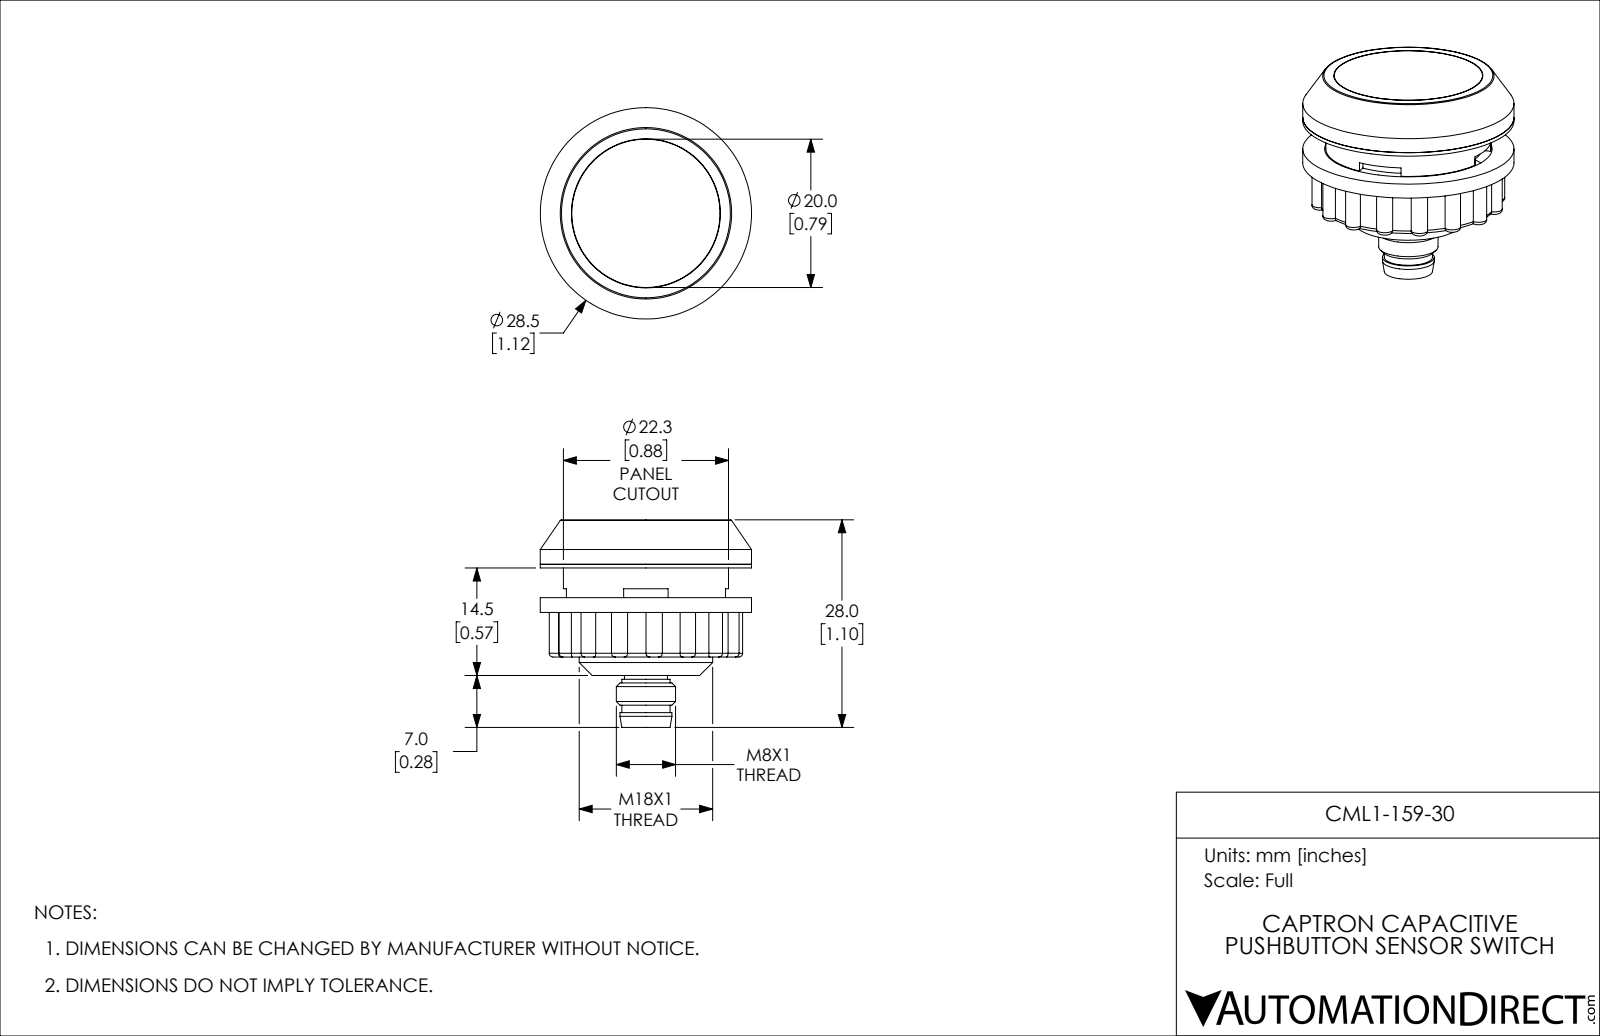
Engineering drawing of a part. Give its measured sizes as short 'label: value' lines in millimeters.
name: CML1-159-30
written by: SolidWorks 2019 (CONFIG_CONTROL_DESIGN)
unit: mm
bodies: 10 solids, 213 faces (39 planar, 99 cylindrical, 75 other)
size: 28.5 × 28.5 × 28
volume: 9 790 mm³; area: 7 226 mm²
holes: 2× ⌀2, 1× ⌀6, 1× ⌀17, 1× ⌀20.1, 1× ⌀22.3, 1× ⌀22.6
bosses: 4× ⌀1, 1× ⌀28.5, 1× ⌀22.28, 1× ⌀18, 1× ⌀8, 1× ⌀7, 1× ⌀6.5, 1× ⌀5.8
rounds: 16× R1.1, 1× R9.9, 1× R12
face distances: 6, 3, 6.5, 10.5, 4, 4.5, 12.5, 7.5, 14.5, 8.2
hole spacings: 5.5, 11
